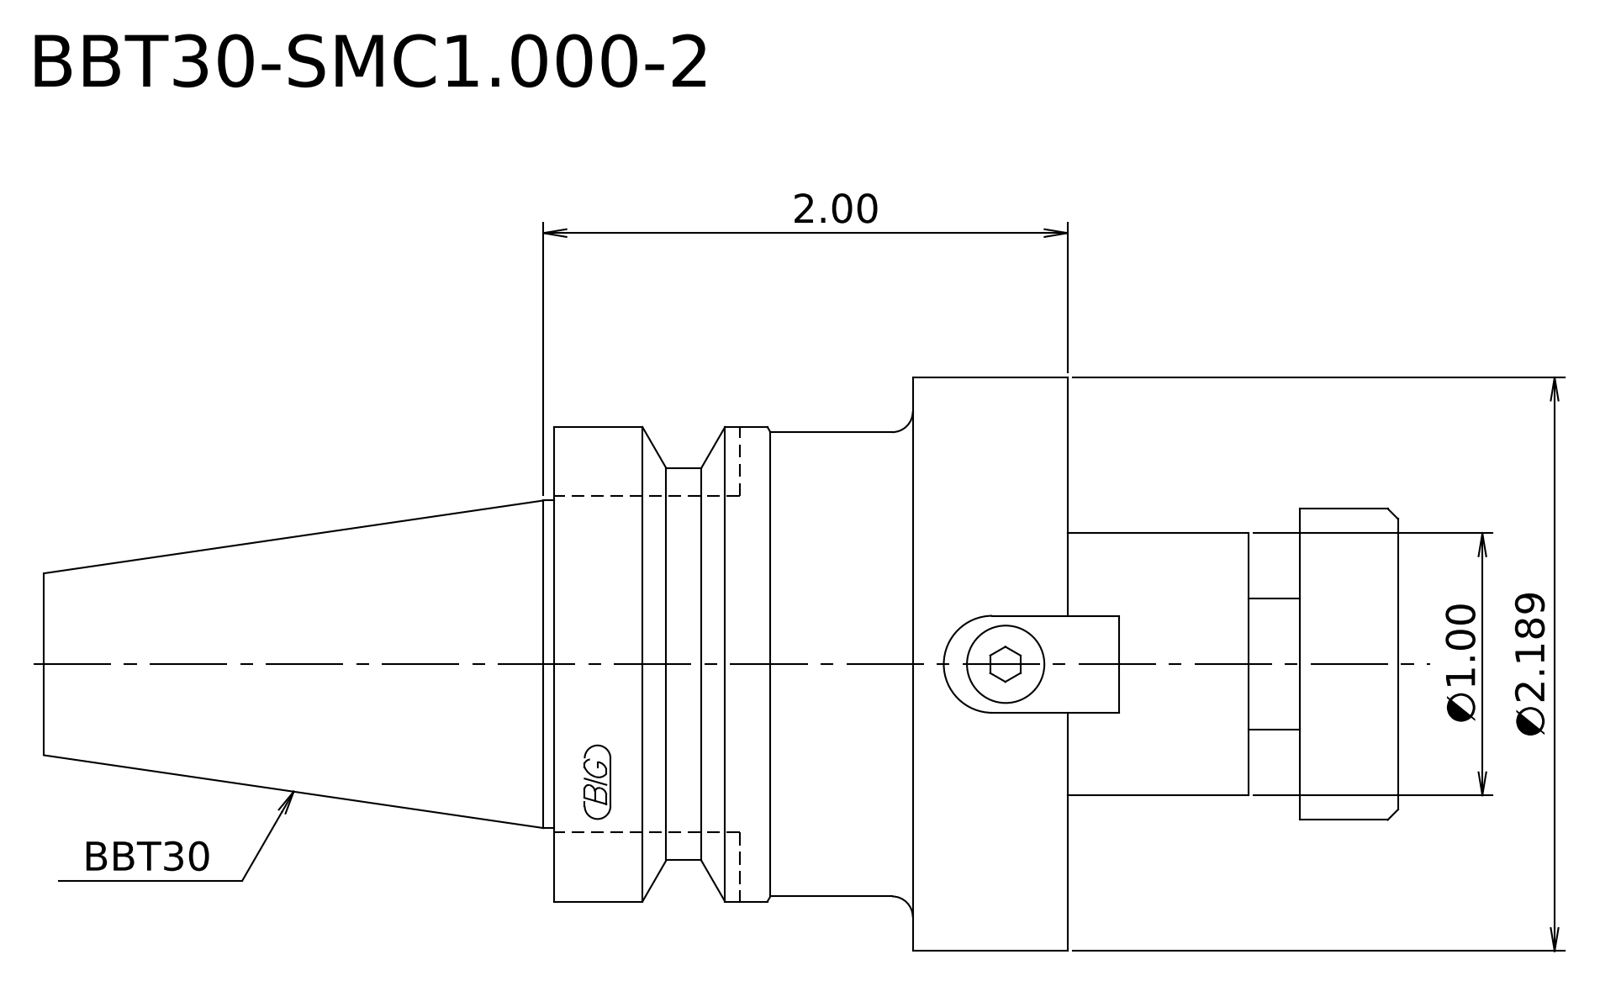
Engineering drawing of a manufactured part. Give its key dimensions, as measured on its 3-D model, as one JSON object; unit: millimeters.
{"part_name": "BBT30-SMC1_000-2", "step_written_by": "SolidWorks 2021 (CONFIG_CONTROL_DESIGN)", "units": "millimeters", "bodies": {"solids": 1, "faces": 26, "planar": 17, "cylindrical": 6, "other": 3}, "overall_size": [104.1, 55.6, 55.6], "volume_mm3": 114286, "surface_area_mm2": 17813, "round_holes": [[11.53, 1]], "round_bosses_or_shafts": [[55.6, 1], [46, 1], [38, 1], [31.75, 1]], "face_to_face_distances": [49.8, 15.8, 34, 99.2, 83.4, 49.4, 9.53, 4.9, 20.7, 54.7]}
